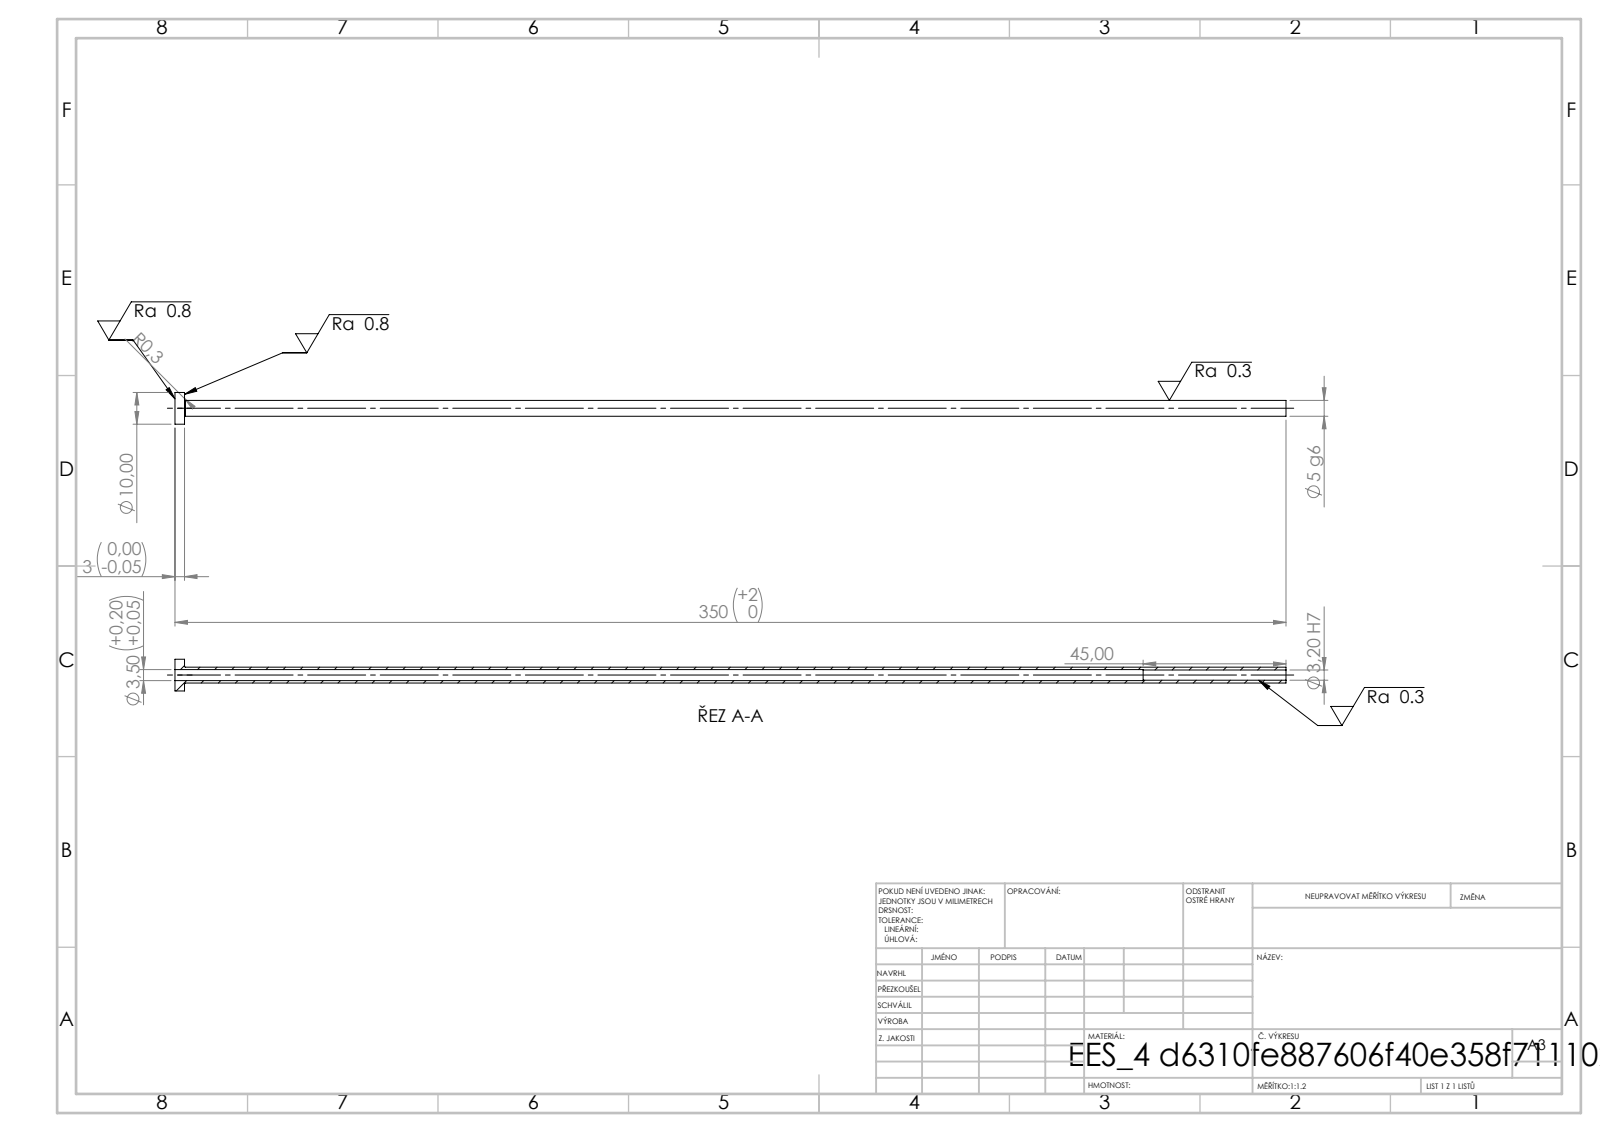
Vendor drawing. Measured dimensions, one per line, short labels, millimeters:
written by: SolidWorks 2019 (CONFIG_CONTROL_DESIGN)
unit: mm
bodies: 1 solid, 14 faces (4 planar, 8 cylindrical, 2 other)
size: 350 × 10 × 10
volume: 3 753 mm³; area: 9 490 mm²
holes: 1× ⌀3.2, 1× ⌀3.5
bosses: 1× ⌀10, 1× ⌀5
face distances: 3, 350, 347, 305, 302, 45
